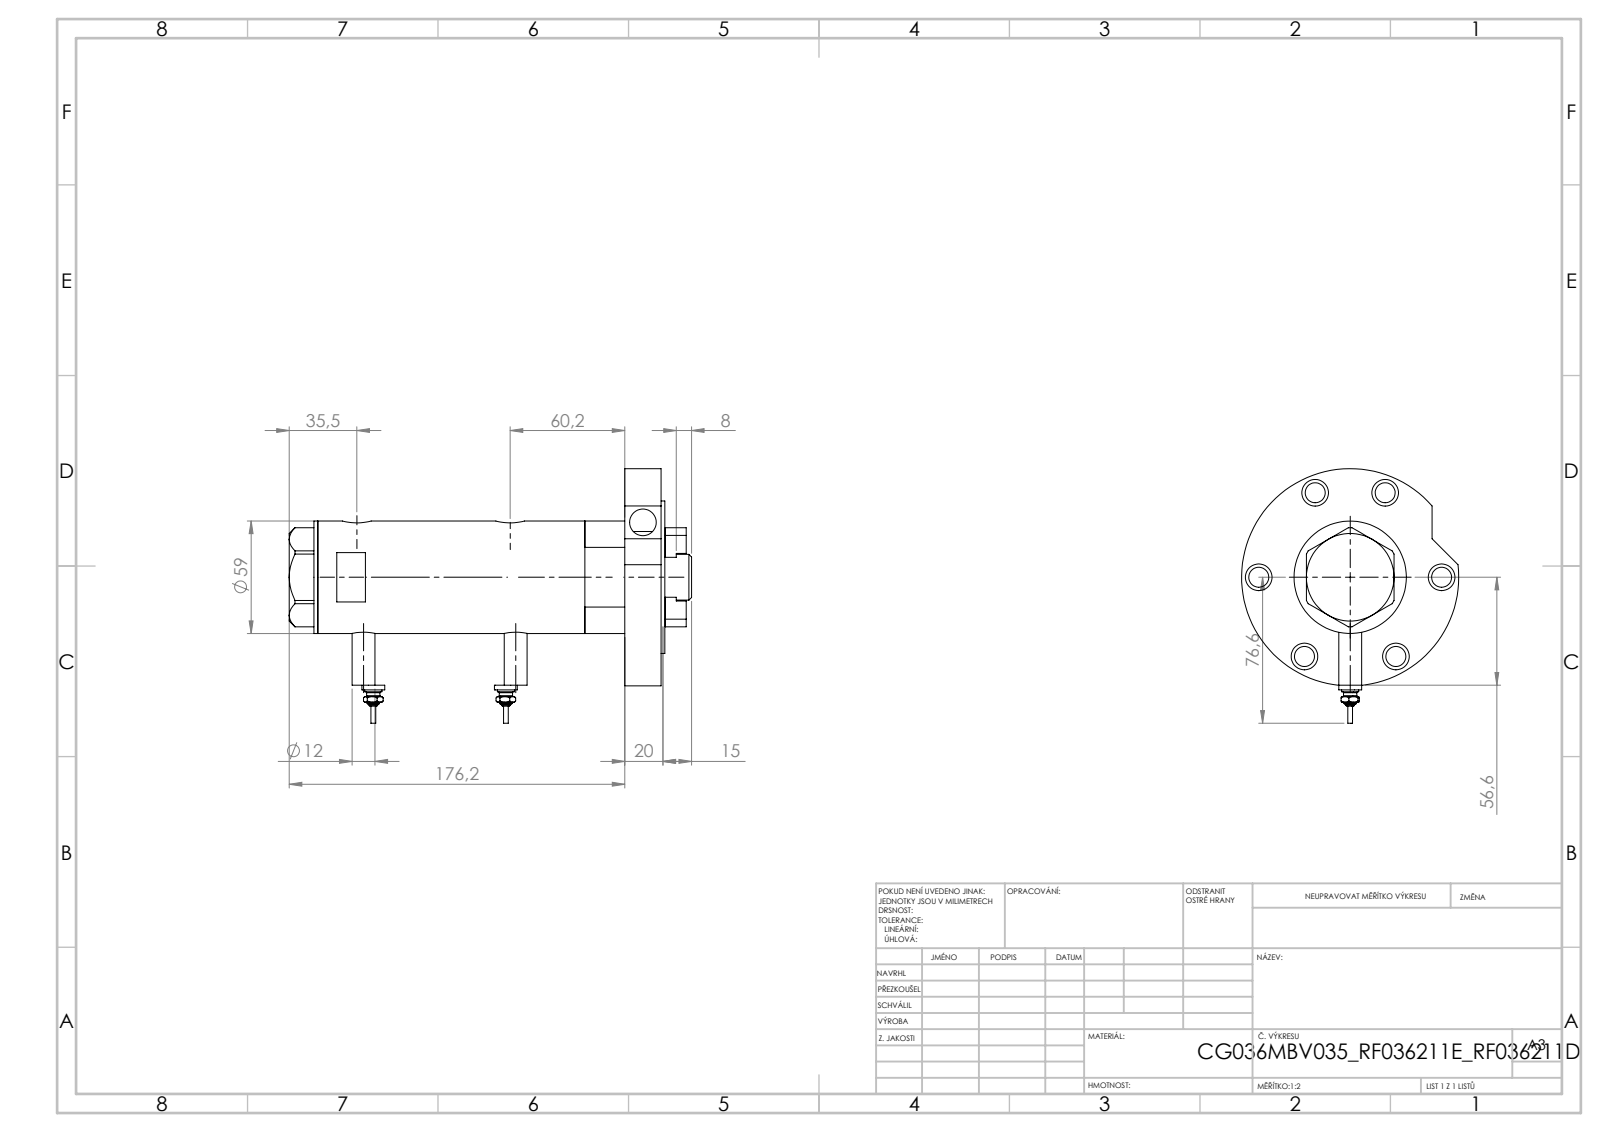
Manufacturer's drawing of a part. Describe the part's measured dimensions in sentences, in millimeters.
The part is named "V270CG_FRONT; V270CG_RF211D; V270CG_RF211E; V270CG_BACK (+3 more)". Its 3-D file was written by "SolidWorks 2019 (CONFIG_CONTROL_DESIGN)". It is 9 solids with 316 faces: 116 planar, 126 cylindrical and 74 other. Overall it measures 198.42 by 118.8 by 114 millimeters. Its volume is 592 688 cubic millimeters and its surface area 134 687 square millimeters. Round holes: 10 of diameter 10.5, 7 of diameter 14, 4 of diameter 6.1, 2 of diameter 5, 2 of diameter 9.73, 2 of diameter 12.5, 2 of diameter 15, 1 of diameter 8.5, 1 of diameter 25, 1 of diameter 26.5, 1 of diameter 36, 1 of diameter 40. Round bosses or shafts: 3 of diameter 12, 2 of diameter 9, 2 of diameter 7, 2 of diameter 4.34, 2 of diameter 2.4, 1 of diameter 114, 1 of diameter 80, 1 of diameter 59. The main face-to-face distances are 19, 2, 166.84, 21, 145.84, 164.84, 92.34, 53.5, 72.5, 74.5. The hole center spacings are 48, 19.92, 46.09, 57.24, 2.9, 3.5, 12, 28.22.
